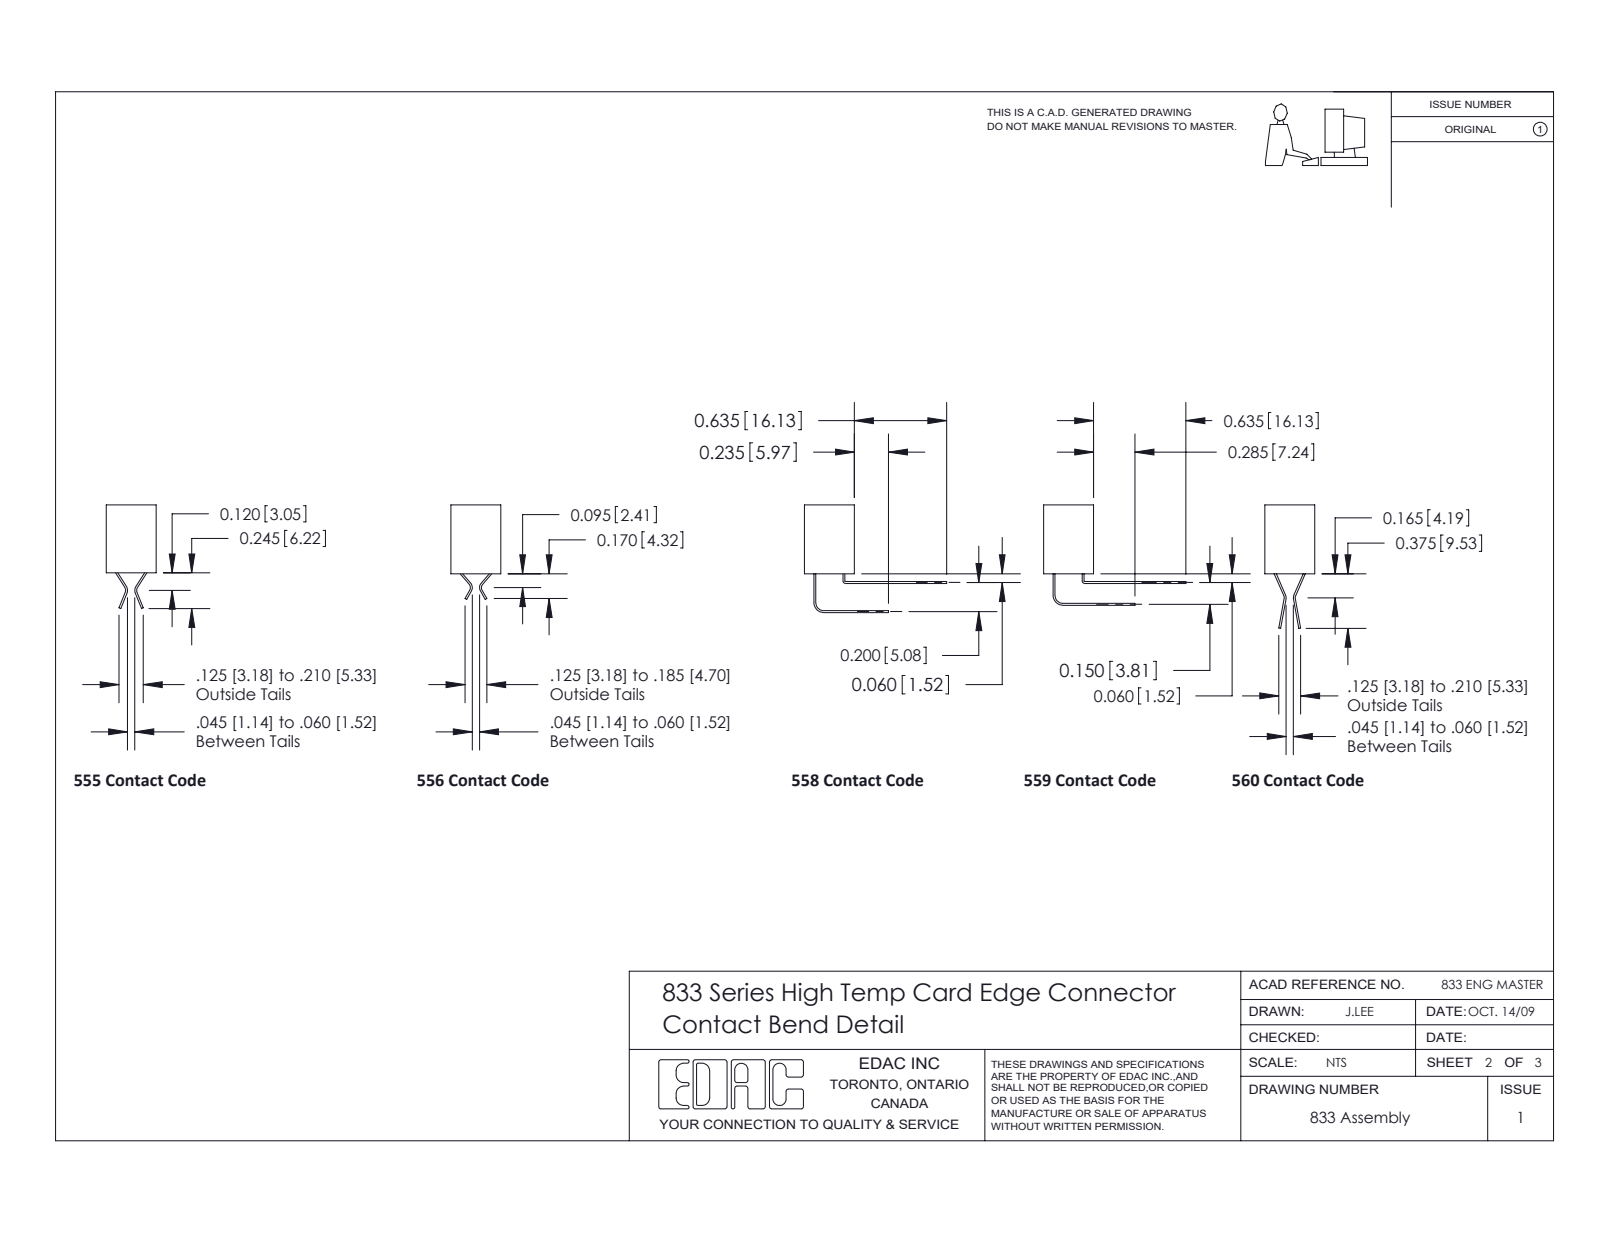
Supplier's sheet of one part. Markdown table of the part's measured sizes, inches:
| quantity | value |
| --- | --- |
| part name | 833 Part_Lugless; 345-292-001_345-293-120; 833-010-520-101 |
| STEP written by | SolidWorks 2020 (CONFIG_CONTROL_DESIGN) |
| units | inches |
| bodies | 11 solids, 726 faces (506 planar, 220 cylindrical, 0 other) |
| overall size | 1.885 × 0.788 × 0.37 |
| volume | 0.313 in³ |
| surface area | 8.049 in² |
| partial cylindrical surfaces (radius × count) | 0.01 × 22, 0.01 × 22, 0.006 × 20, 0.007 × 6, 0.031 × 6, 0.026 × 3, 0.014 × 1, 0.022 × 1 |
| main face-to-face distances | 0.37, 0.156, 0.148, 0.222, 0.05, 0.298, 0.072, 0.076, 0.15, 0.312 |
